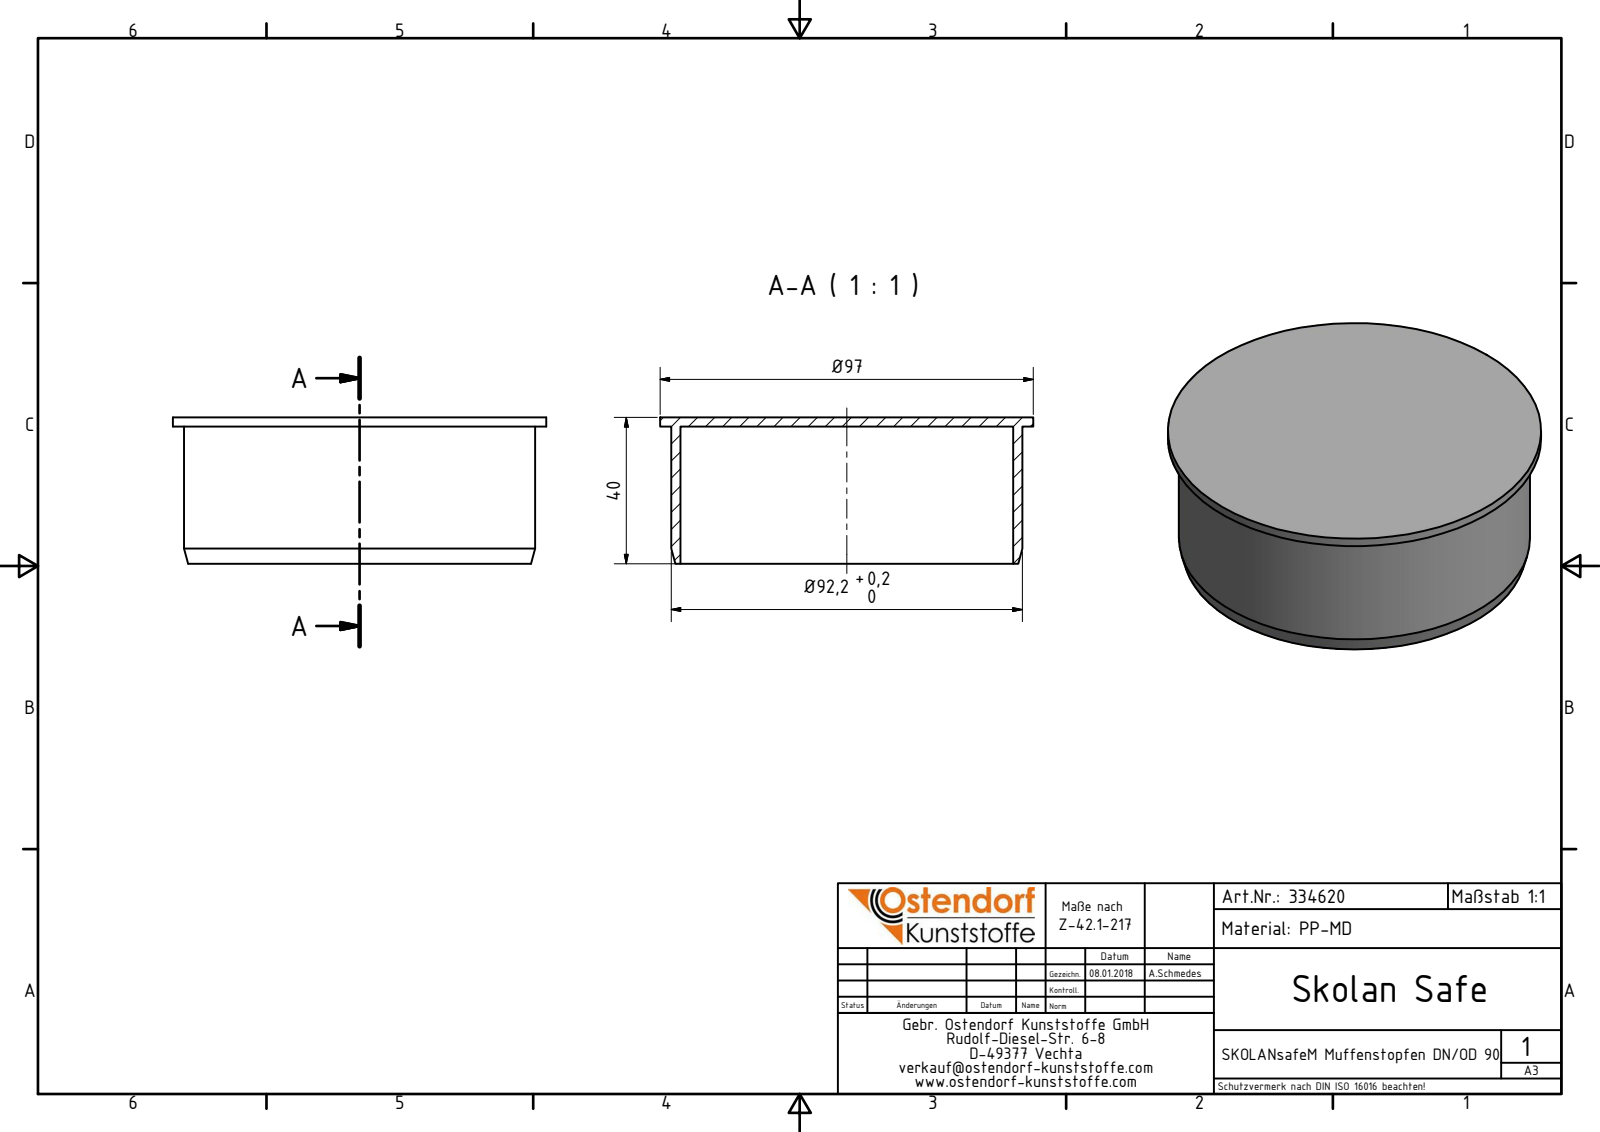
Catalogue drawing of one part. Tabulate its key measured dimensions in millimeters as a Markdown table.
| quantity | value |
| --- | --- |
| part name | 334620 SKOLANsafeM Muffenstopfen DN_OD 90 |
| STEP written by | Autodesk Inventor 2016 (AUTOMOTIVE_DESIGN) |
| units | millimeters |
| bodies | 1 solid, 8 faces (4 planar, 3 cylindrical, 1 other) |
| overall size | 98 × 98 × 38.4 |
| volume | 41 862 mm³ |
| surface area | 35 857 mm² |
| round holes (diameter × count) | 87.4 × 1 |
| round bosses / shafts (diameter × count) | 98 × 1, 92.2 × 1 |
| main face-to-face distances | 2.4, 36, 38.4 |
